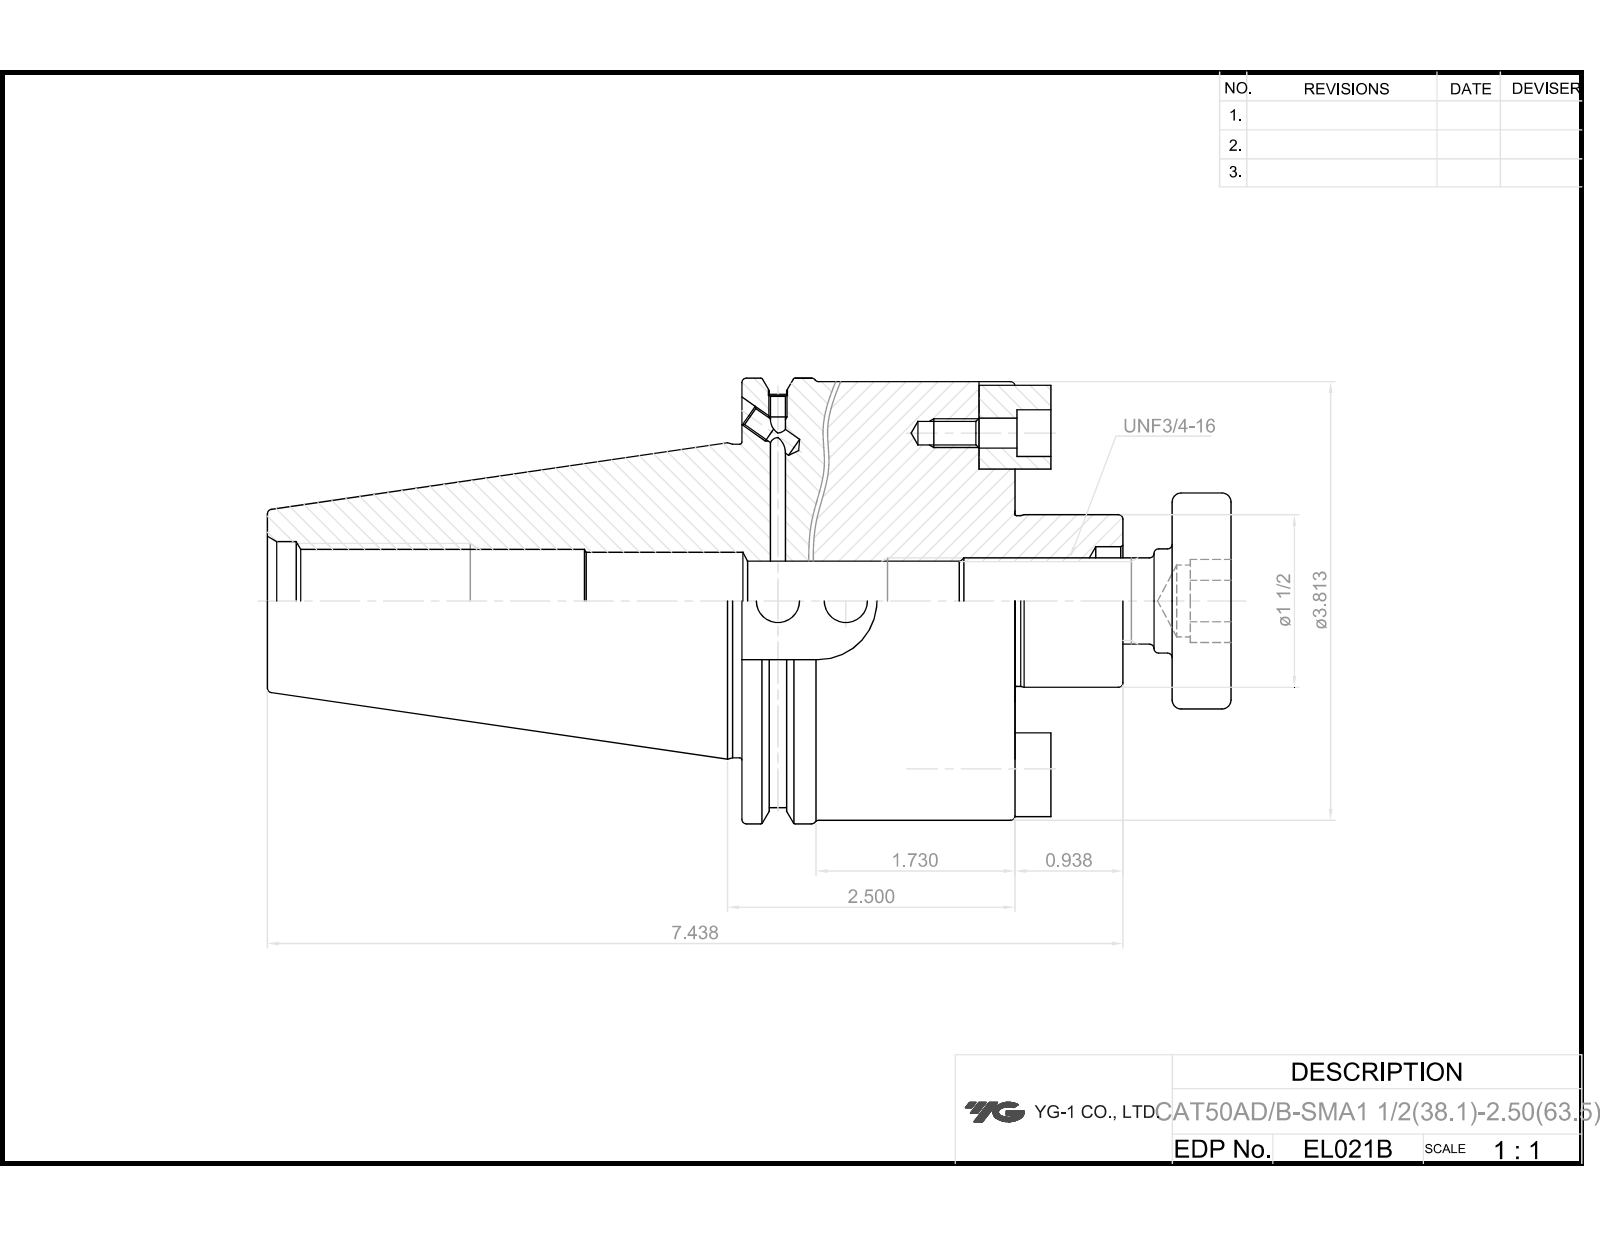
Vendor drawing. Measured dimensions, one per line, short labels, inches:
name: LO-CAT50ADB-SMA38.1-63.5; DRIVE KEY-15.875x15.875x18.5; HEX'' WRENCH BOLT-UNC1_4-20x5_8L; COLLAR BOLT-UNF3_4-16x47L
written by: Autodesk Inventor 2025 (AP242_MANAGED_MODEL_BASED_3D_ENGINEERING_MIM_LF)
unit: in
bodies: 6 solids, 165 faces (85 planar, 46 cylindrical, 34 other)
size: 8.344 × 3.875 × 3.813
volume: 42 in³; area: 126.2 in²
holes: 2× ⌀0.128, 2× ⌀0.163, 2× ⌀0.165, 2× ⌀0.196, 2× ⌀0.197, 2× ⌀0.26, 2× ⌀0.406, 1× ⌀0.375, 1× ⌀0.625, 1× ⌀0.682, 1× ⌀0.865, 1× ⌀0.945
bosses: 2× ⌀0.375, 2× ⌀0.25, 1× ⌀3.875, 1× ⌀3.813, 1× ⌀3.594, 1× ⌀2.726, 1× ⌀1.878, 1× ⌀1.5
rounds: 2× R0.312, 1× R0.51
face distances: 2.375, 4.219, 1.844, 3.707, 1.332, 0.512, 2.062, 0.313, 1.645, 2.157
hole spacings: 1.459, 2.918
